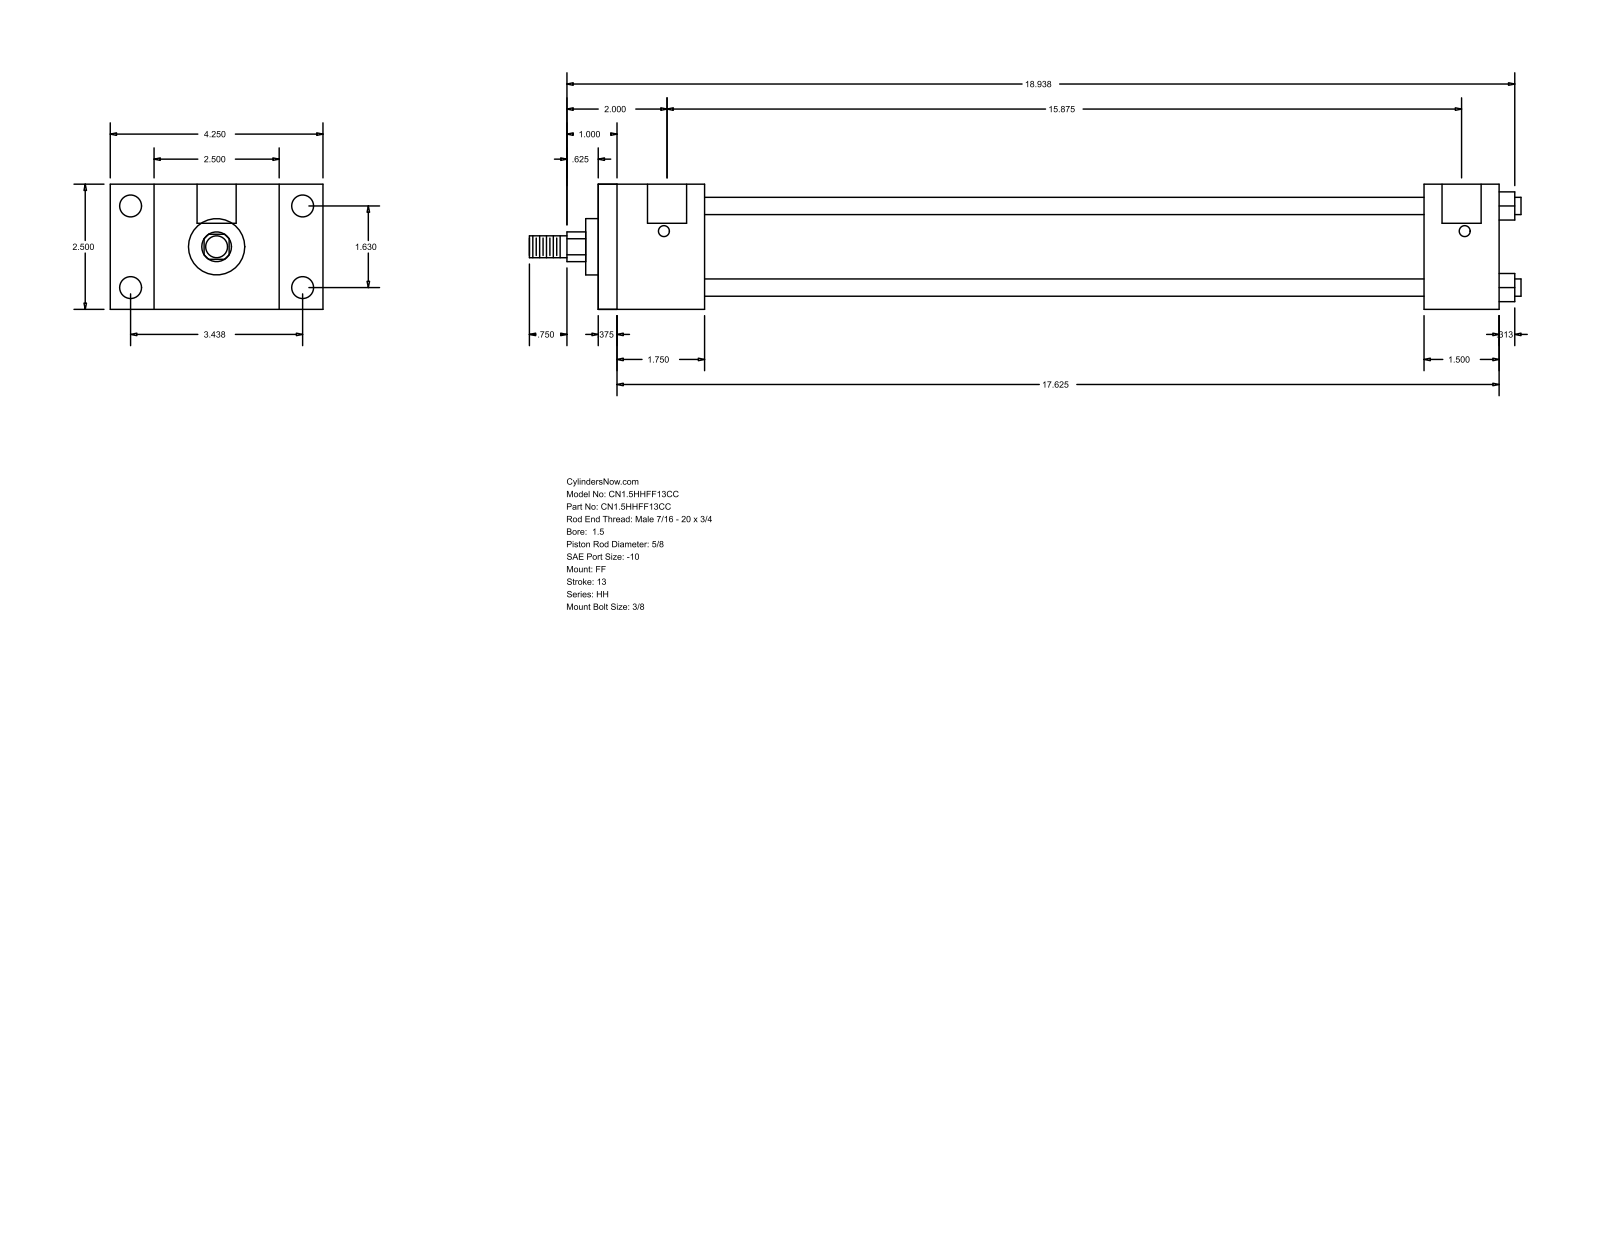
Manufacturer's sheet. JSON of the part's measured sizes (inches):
{"part_name": "HH_FF__0150_0.625", "step_written_by": "GSSL Pune (CONFIG_CONTROL_DESIGN)", "units": "inches", "bodies": {"solids": 0, "faces": 92, "planar": 64, "cylindrical": 28, "other": 0}, "overall_size": [19.813, 4.25, 2.5], "round_holes": [[0.219, 4], [0.438, 4], [0.781, 2]], "round_bosses_or_shafts": [[0.345, 4], [1.75, 1], [1.125, 1], [0.625, 1], [0.437, 1]], "partial_cylinders_radius": [[0.297, 1]], "face_to_face_distances": [2.5, 18, 0.375, 17.625, 1.75, 2.125, 15.875, 16.5, 16.125, 14.375], "hole_center_spacings": [0.063, 1.63, 3.438, 3.805, 15.937, 16, 15.875]}
